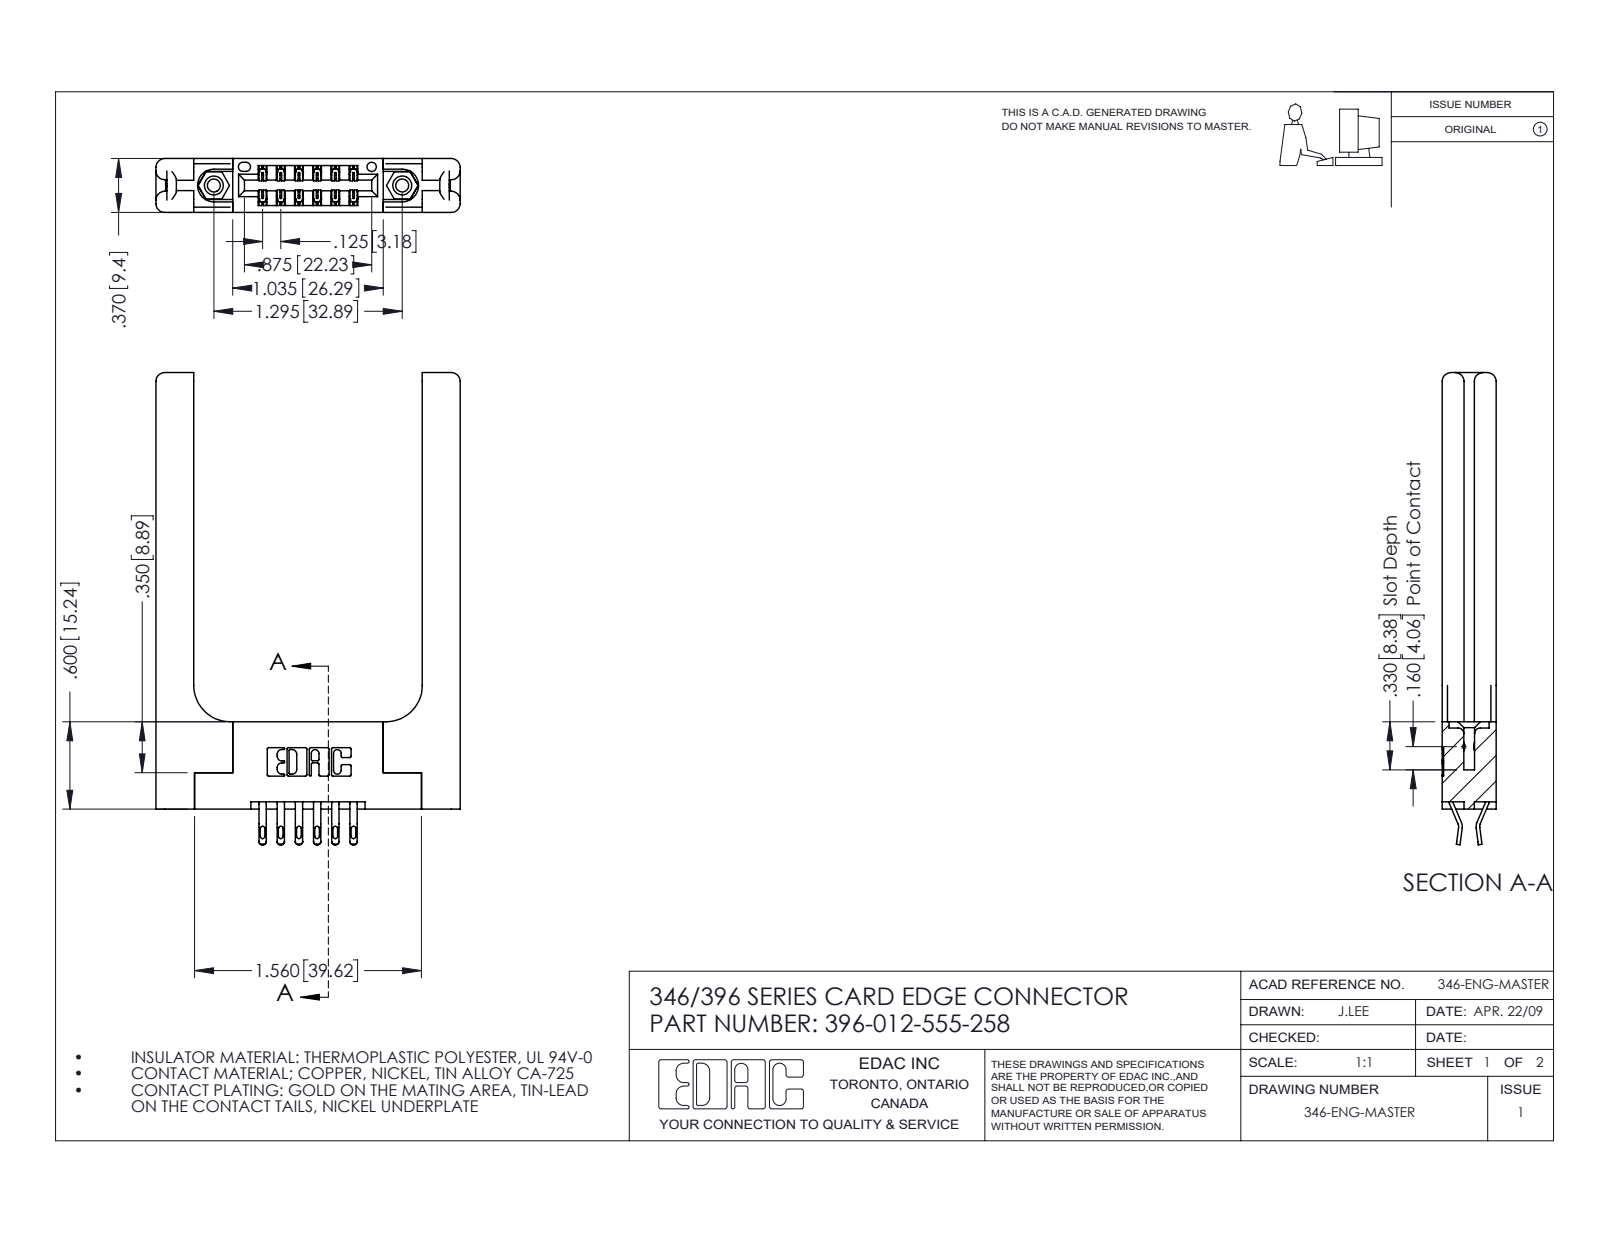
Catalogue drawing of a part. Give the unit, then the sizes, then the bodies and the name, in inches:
Units: inches
Overall size (bounding box): 3.245 × 2.091 × 0.37
Round holes (diameter × count): ⌀0.089 ×2, ⌀0.125 ×2, ⌀0.156 ×2, ⌀0.064 ×1
Round bosses / shafts (diameter × count): ⌀0.155 ×2
Partial cylindrical surfaces — rounded edges, fillets, slot ends (radius × count): R0.016 ×24, R0.02 ×24, R0.01 ×22, R0.006 ×18, R0.06 ×16, R0.007 ×6, R0.031 ×6, R0.026 ×3
Main face-to-face distances: 0.37, 0.15, 0.22, 0.25, 0.072, 0.148, 1.571, 0.102, 0.048, 0.322
Hole centre spacings: 0.246, 1.092, 1.295
Volume: 0.758 in³ · Surface area: 17.54 in²
Bodies: 17 solids, 1074 faces (620 planar, 394 cylindrical, 60 other)
Part name (STEP PRODUCT): 346 Part_Flush Mounting Lugs - 0.156 Dia-TH; 396-012-555-258; 345-250-001_345-250-001-102; 346-220-058_345-220-058 (+1 more)
STEP written by: SolidWorks 2016 (CONFIG_CONTROL_DESIGN)
